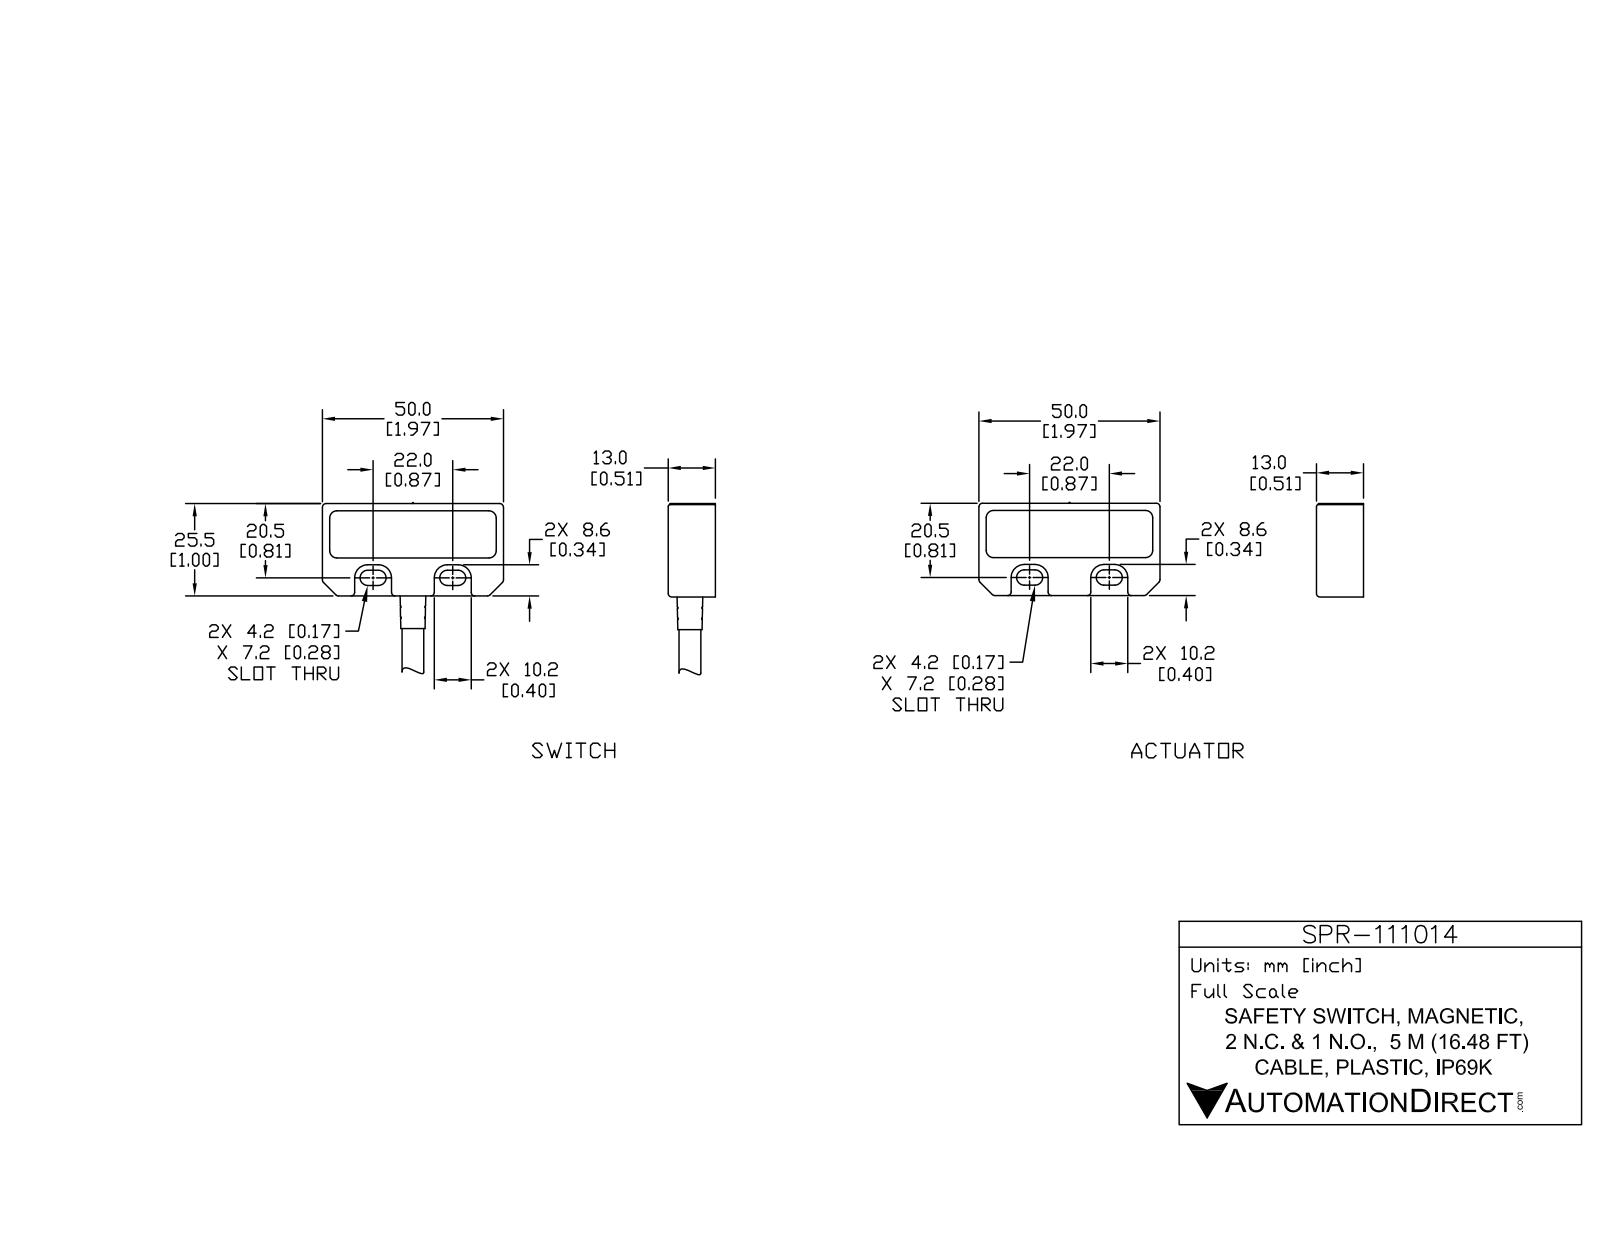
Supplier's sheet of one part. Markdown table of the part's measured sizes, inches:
| quantity | value |
| --- | --- |
| part name | SPR-111014_1; SPR-111014; SPR-111014_2 |
| STEP written by | SolidWorks 2017 (AUTOMOTIVE_DESIGN) |
| units | inches |
| bodies | 4 solids, 191 faces (61 planar, 80 cylindrical, 50 other) |
| overall size | 5.885 × 1.969 × 0.524 |
| volume | 2.063 in³ |
| surface area | 18.22 in² |
| round bosses / shafts (diameter × count) | 0.236 × 1 |
| partial cylindrical surfaces (radius × count) | 0.039 × 36, 0.079 × 8, 0.083 × 8, 0.142 × 8, 0.02 × 2 |
| main face-to-face distances | 0.512, 1.004, 1.043, 0.524, 0.039, 1.969, 2.047, 0.165, 0.177, 0.346 |
